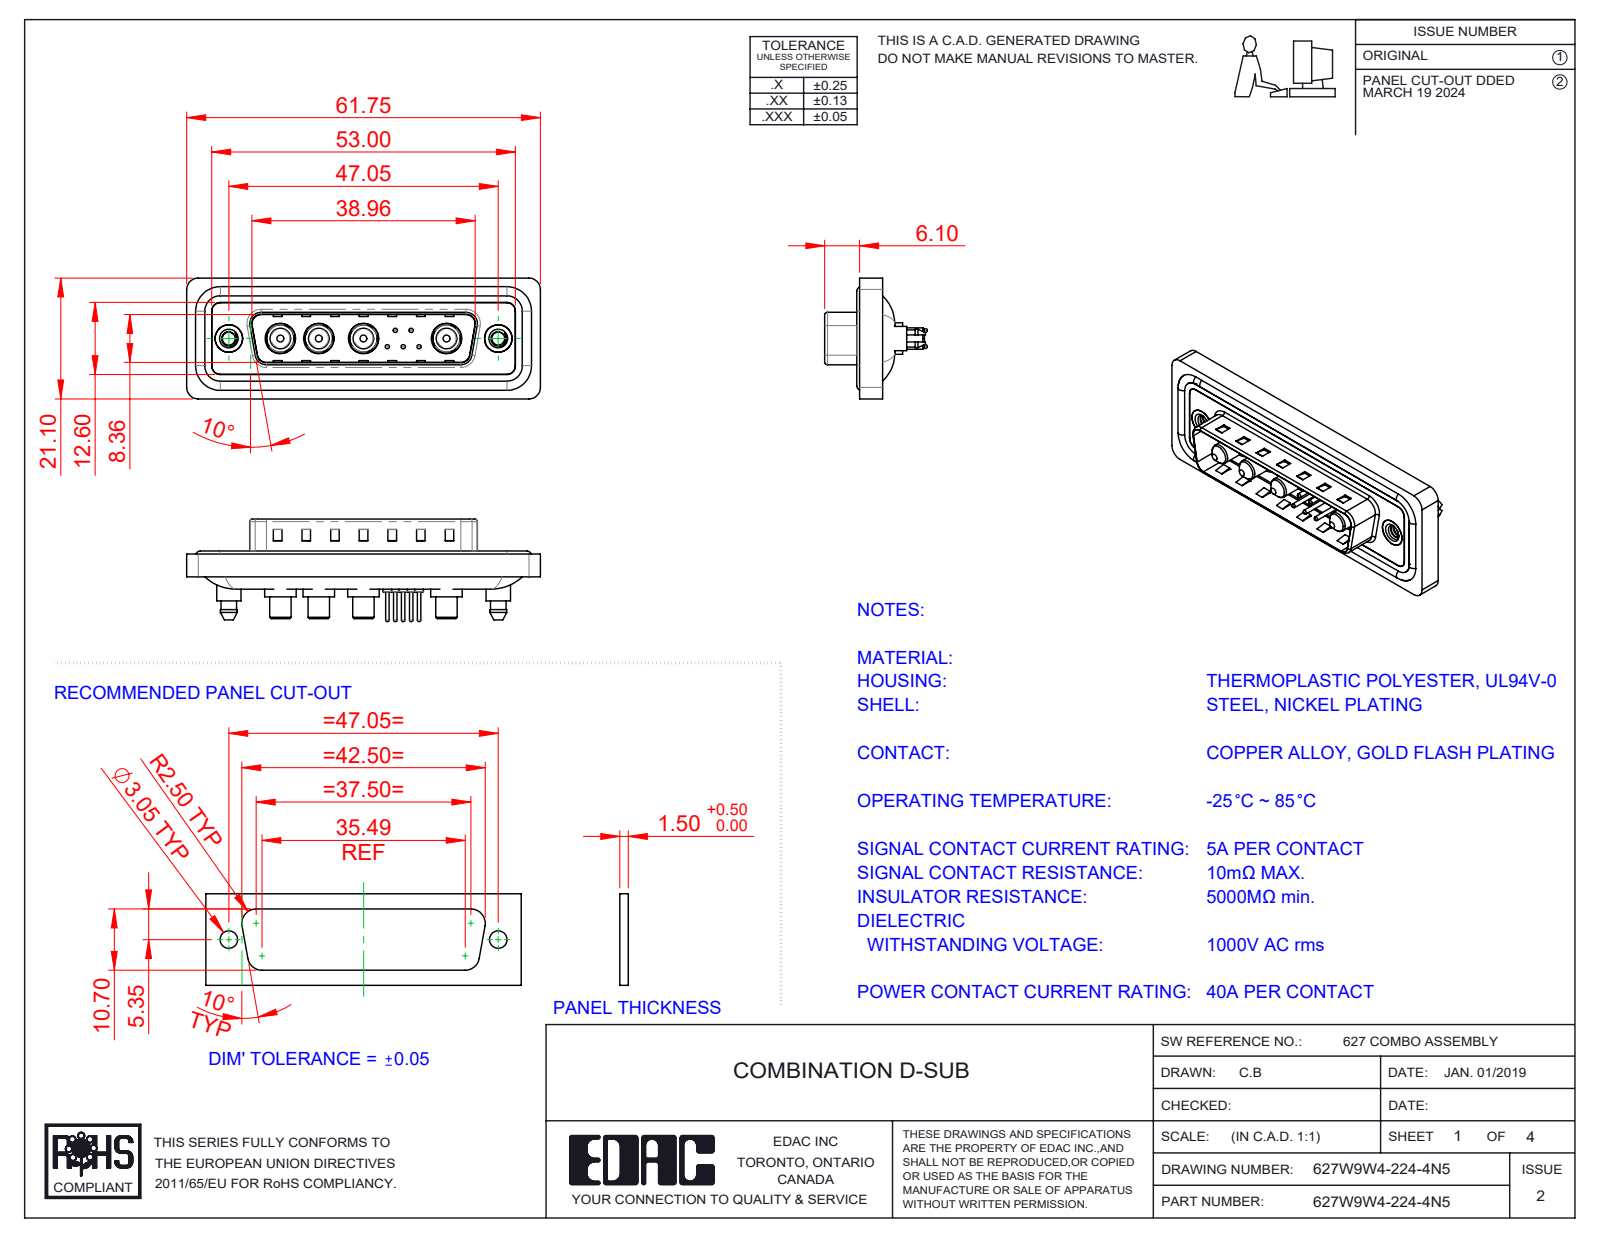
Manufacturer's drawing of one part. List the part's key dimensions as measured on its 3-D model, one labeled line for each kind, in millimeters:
Part name (STEP PRODUCT): 627Combo Contact Row 2_24; 627Combo Shell Front_25 Contacts; 627Combo Waterproof Housing_25 Contacts; 627Combo Threaded Boardlock_5 (+5 more)
STEP written by: SolidWorks 2023 (CONFIG_CONTROL_DESIGN)
Units: millimetres
Bodies: 20 solids, 874 faces (300 planar, 366 cylindrical, 208 other)
Overall size (bounding box): 61.75 × 21.1 × 17.9
Volume: 7 612 mm³ · Surface area: 12 212 mm²
Round holes (diameter × count): ⌀0.75 ×5, ⌀1.6 ×5, ⌀2 ×5, ⌀4.85 ×4, ⌀5.3 ×4, ⌀2.26 ×2, ⌀4 ×2, ⌀4.8 ×2, ⌀5 ×2
Round bosses / shafts (diameter × count): ⌀1.5 ×5, ⌀0.6 ×5, ⌀5.5 ×4, ⌀5.2 ×4, ⌀4.75 ×4, ⌀3.75 ×4, ⌀3.6 ×4, ⌀1.6 ×4
Partial cylindrical surfaces — rounded edges, fillets, slot ends (radius × count): R1.5 ×24, R2 ×18, R1.6 ×10, R0.5 ×8, R0.25 ×4, R0.6 ×4, R0.65 ×4, R0.9 ×4
Main face-to-face distances: 0.4, 1.5, 1.1, 0.5, 3.1, 1.6, 2.9, 0.82, 9.58, 5.65
Hole centre spacings: 3.16, 2.77, 5.04, 14.51, 2.78, 4.4, 4.41, 5
